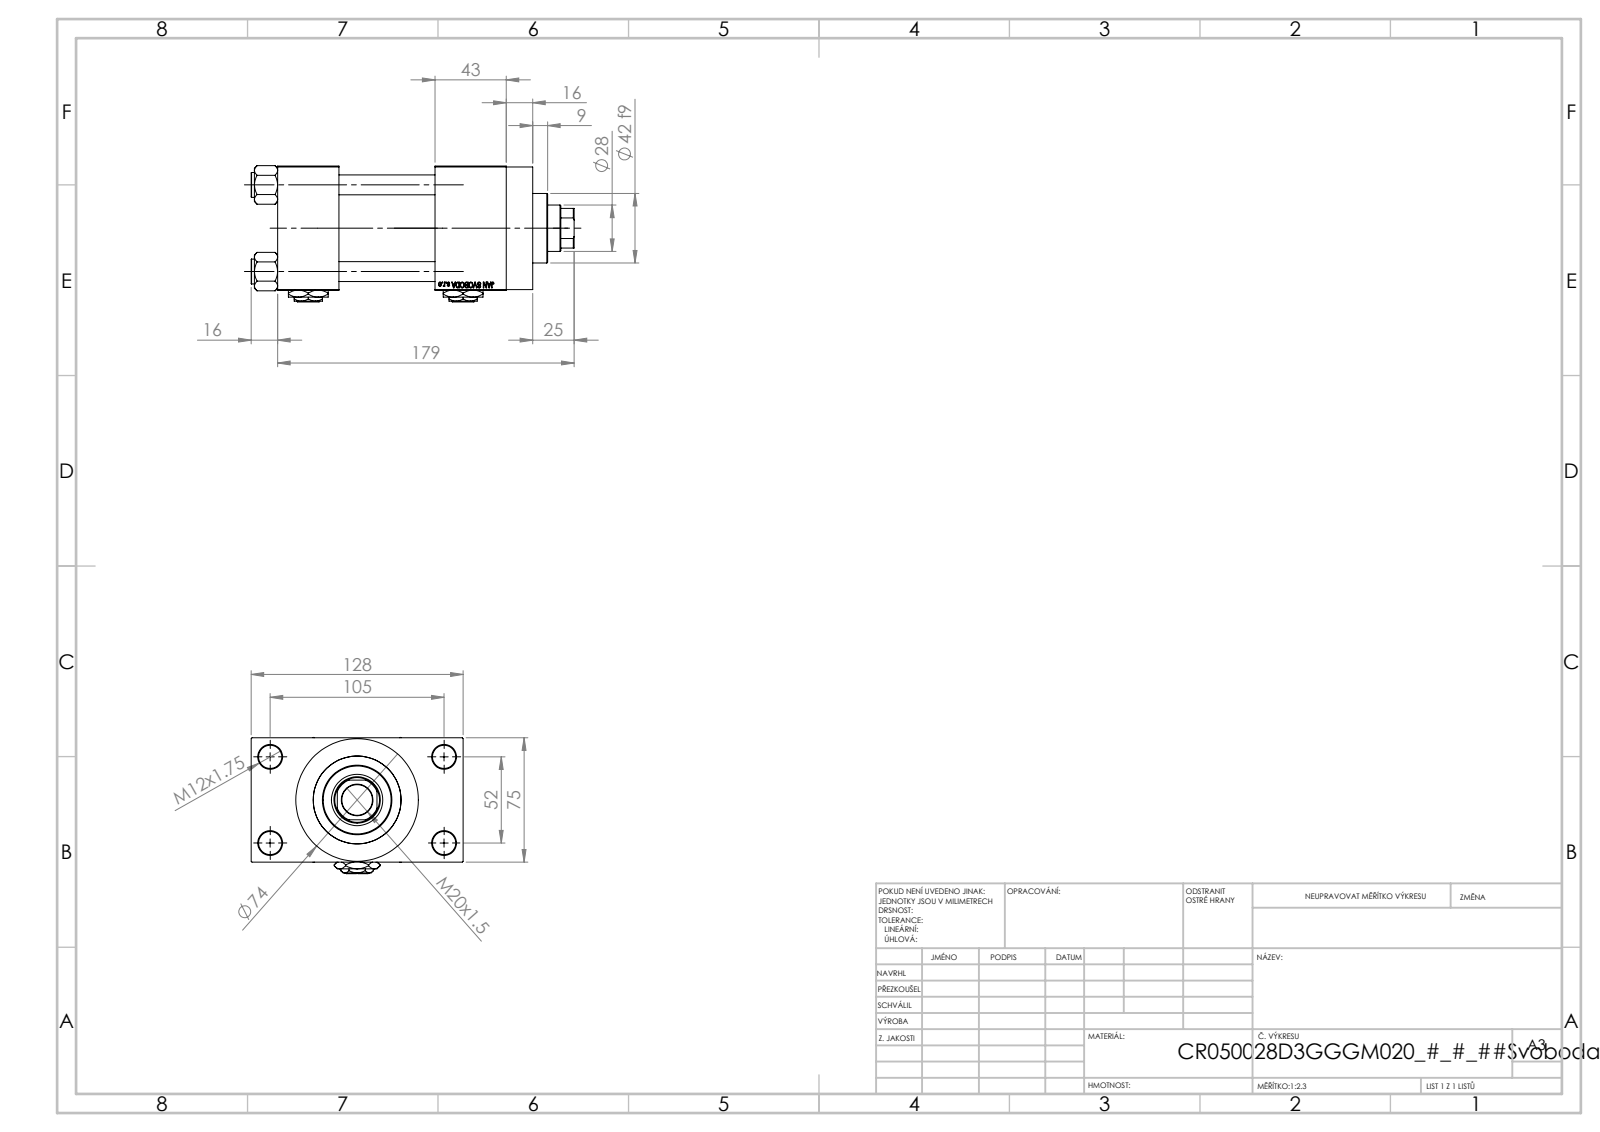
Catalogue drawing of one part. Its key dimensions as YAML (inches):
part_name: "V215CR_D_Body; V215CR_D_TYCINKA; V215CR_VCP_D; Zatka_pro_OIL_PORT (+2 more)"
step_written_by: "SolidWorks 2019 (CONFIG_CONTROL_DESIGN)"
units: inches
bodies: {solids: 13, faces: 1205, planar: 545, cylindrical: 100, other: 560}
overall_size: [7.677, 5.039, 3.239]
volume: 49.48
surface_area: 268.3
round_holes:
  - {diameter: 0.472, count: 4}
  - {diameter: 0.551, count: 4}
  - {diameter: 0.276, count: 2}
  - {diameter: 0.825, count: 2}
  - {diameter: 1.181, count: 2}
  - {diameter: 0.728, count: 1}
  - {diameter: 1.102, count: 1}
  - {diameter: 1.22, count: 1}
  - {diameter: 1.614, count: 1}
  - {diameter: 1.969, count: 1}
  - {diameter: 2.087, count: 1}
round_bosses_or_shafts:
  - {diameter: 0.591, count: 4}
  - {diameter: 2.913, count: 1}
  - {diameter: 2.205, count: 1}
  - {diameter: 1.654, count: 1}
partial_cylinders:
  - {radius: 0.531, count: 1}
face_to_face_distances: [2.953, 2.283, 1.457, 3.74, 3.996, 1.043, 5.433, 3.976, 1.693, 0.63]
hole_center_spacings: [1.037, 1.456, 2.059, 2.3, 2.307, 3.096, 3.715, 2.047]
